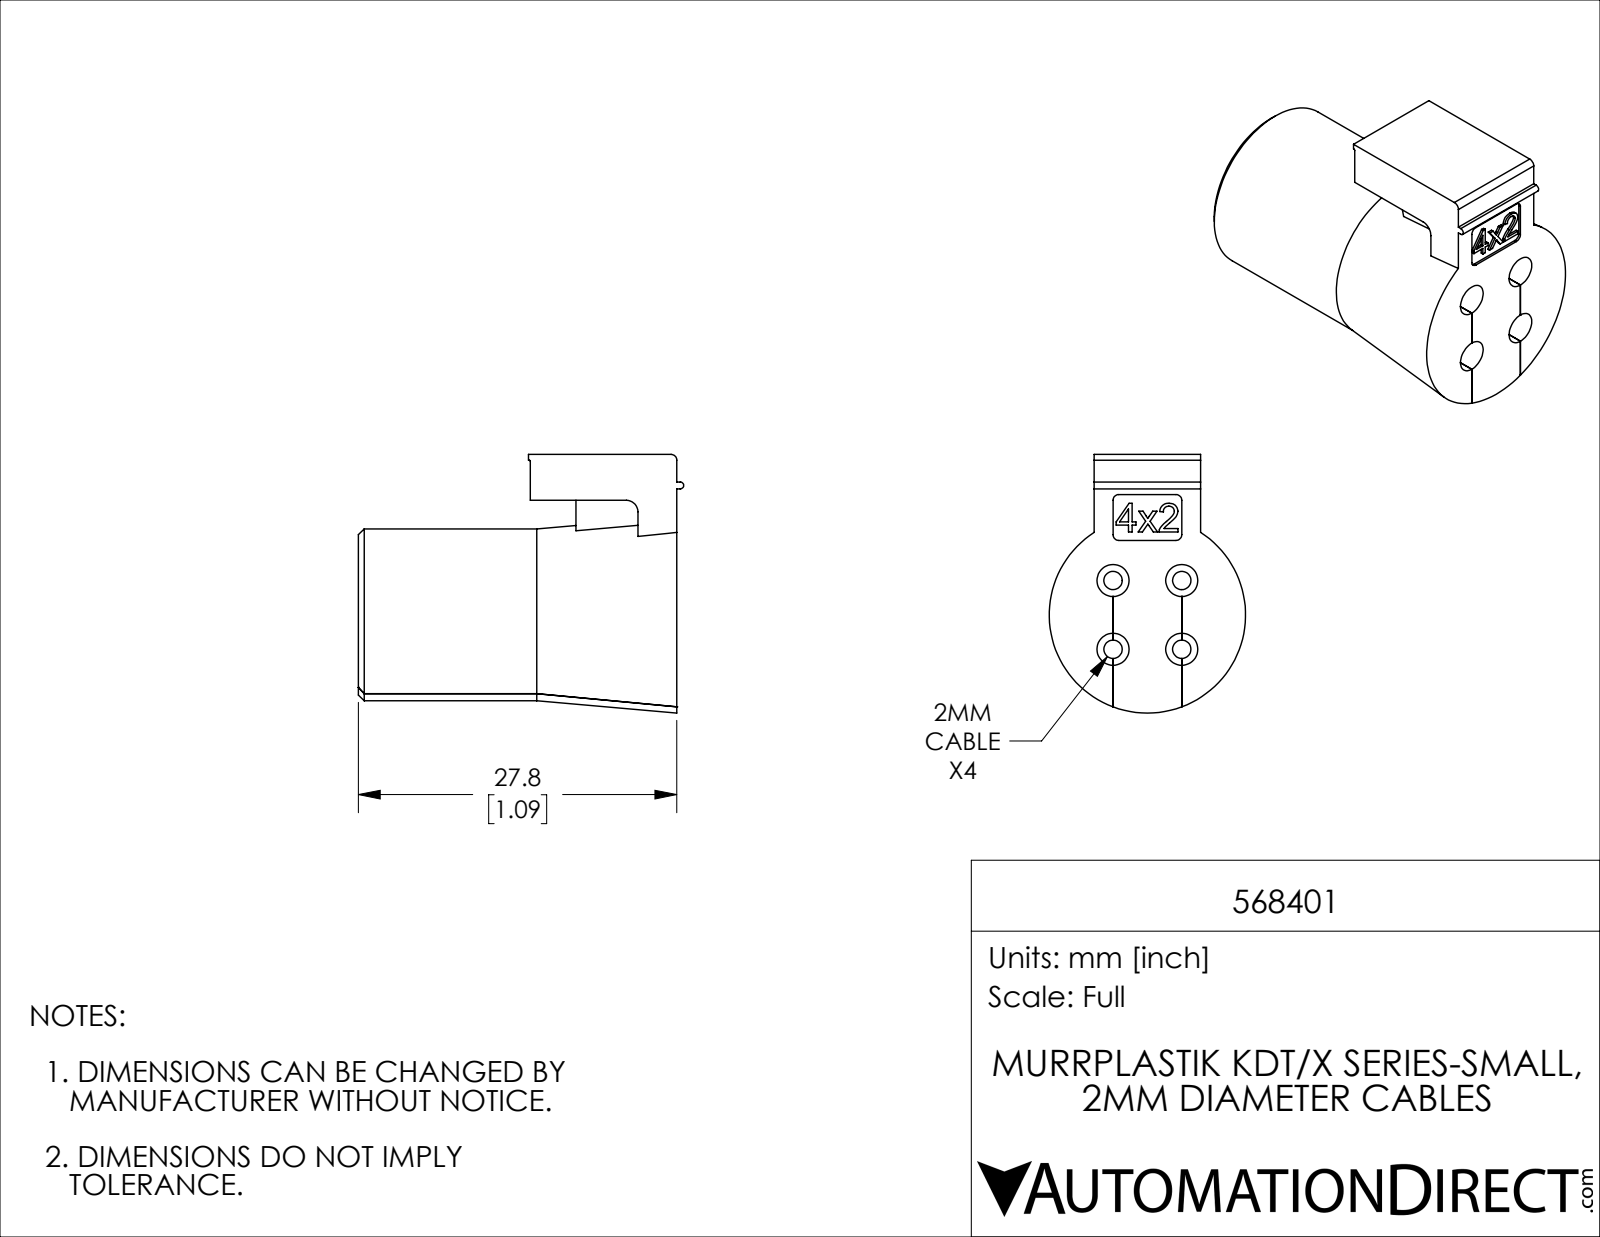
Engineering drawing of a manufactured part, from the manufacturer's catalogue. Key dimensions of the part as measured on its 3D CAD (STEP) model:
Part name (STEP PRODUCT): 568401
STEP written by: SolidWorks 2019 (CONFIG_CONTROL_DESIGN)
Units: inches
Bodies: 1 solid, 145 faces (65 planar, 45 cylindrical, 35 other)
Overall size (bounding box): 1.118 × 0.889 × 0.675
Volume: 0.315 in³ · Surface area: 5.792 in²
Round holes (diameter × count): ⌀0.063 ×4, ⌀0.11 ×4
Round bosses / shafts (diameter × count): ⌀0.591 ×1
Partial cylindrical surfaces — rounded edges, fillets, slot ends (radius × count): R0.02 ×5, R0.004 ×1, R0.012 ×1, R0.039 ×1
Main face-to-face distances: 0.237, 0.236, 0.237, 1.094, 0.065, 0.065, 0.301, 0.302, 0.157, 0.366
Hole centre spacings: 0.236, 0.334
